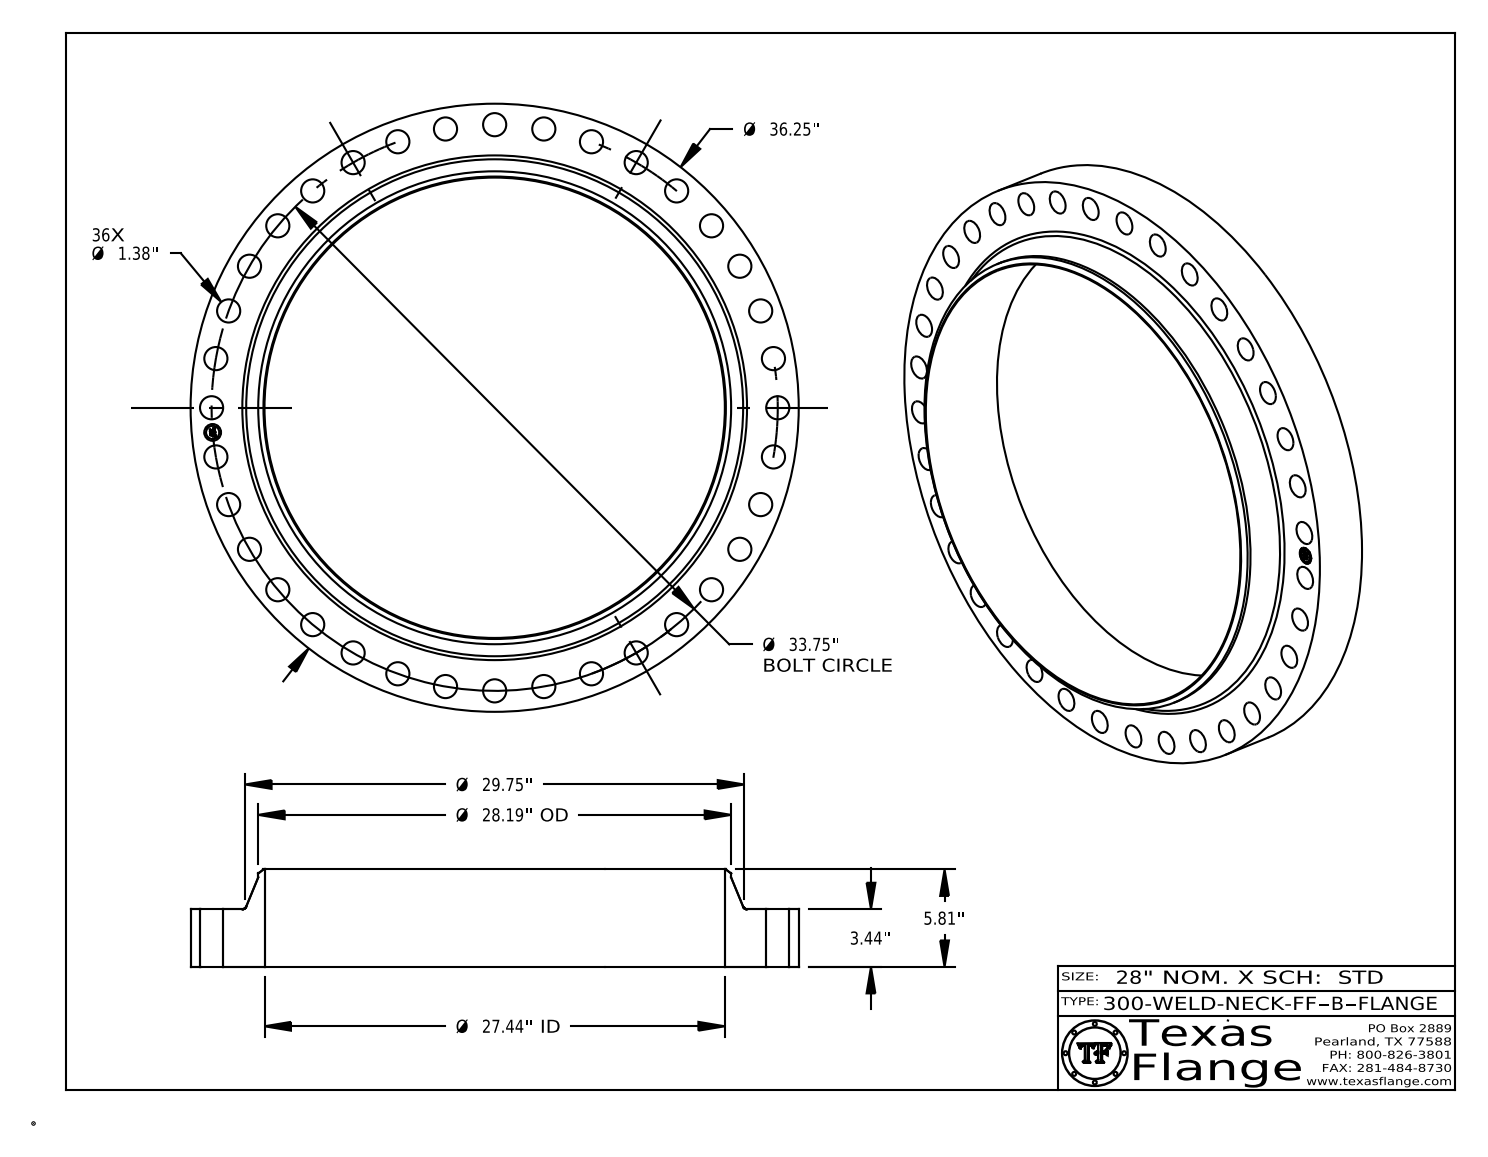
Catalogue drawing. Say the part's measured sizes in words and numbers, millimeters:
The part is named "300-WELD-NECK-FF, Series B". Its 3-D file was written by "CATIA V5 STEP AP214 (AUTOMOTIVE_DESIGN)". It is 1 solid with 472 faces: 368 planar, 98 cylindrical and 6 other. Overall it measures 920.8 by 920.8 by 147.6 millimeters. Its volume is 24 120 000 cubic millimeters and its surface area 1 512 000 square millimeters. Round holes: 36 of diameter 35.1, 1 of diameter 25.4, 1 of diameter 697. Round bosses or shafts: 8 of diameter 1.5, 1 of diameter 920.8, 1 of diameter 716, 1 of diameter 20. The main face-to-face distances are 87.4, 147.6, 60.2, 0.4, 87, 60.6, 7.6, 7.4, 1.4, 4.9. The hole center spacings are 428.6, 854, 828, 428.6, 606.2, 74.7, 551, 656.7.
